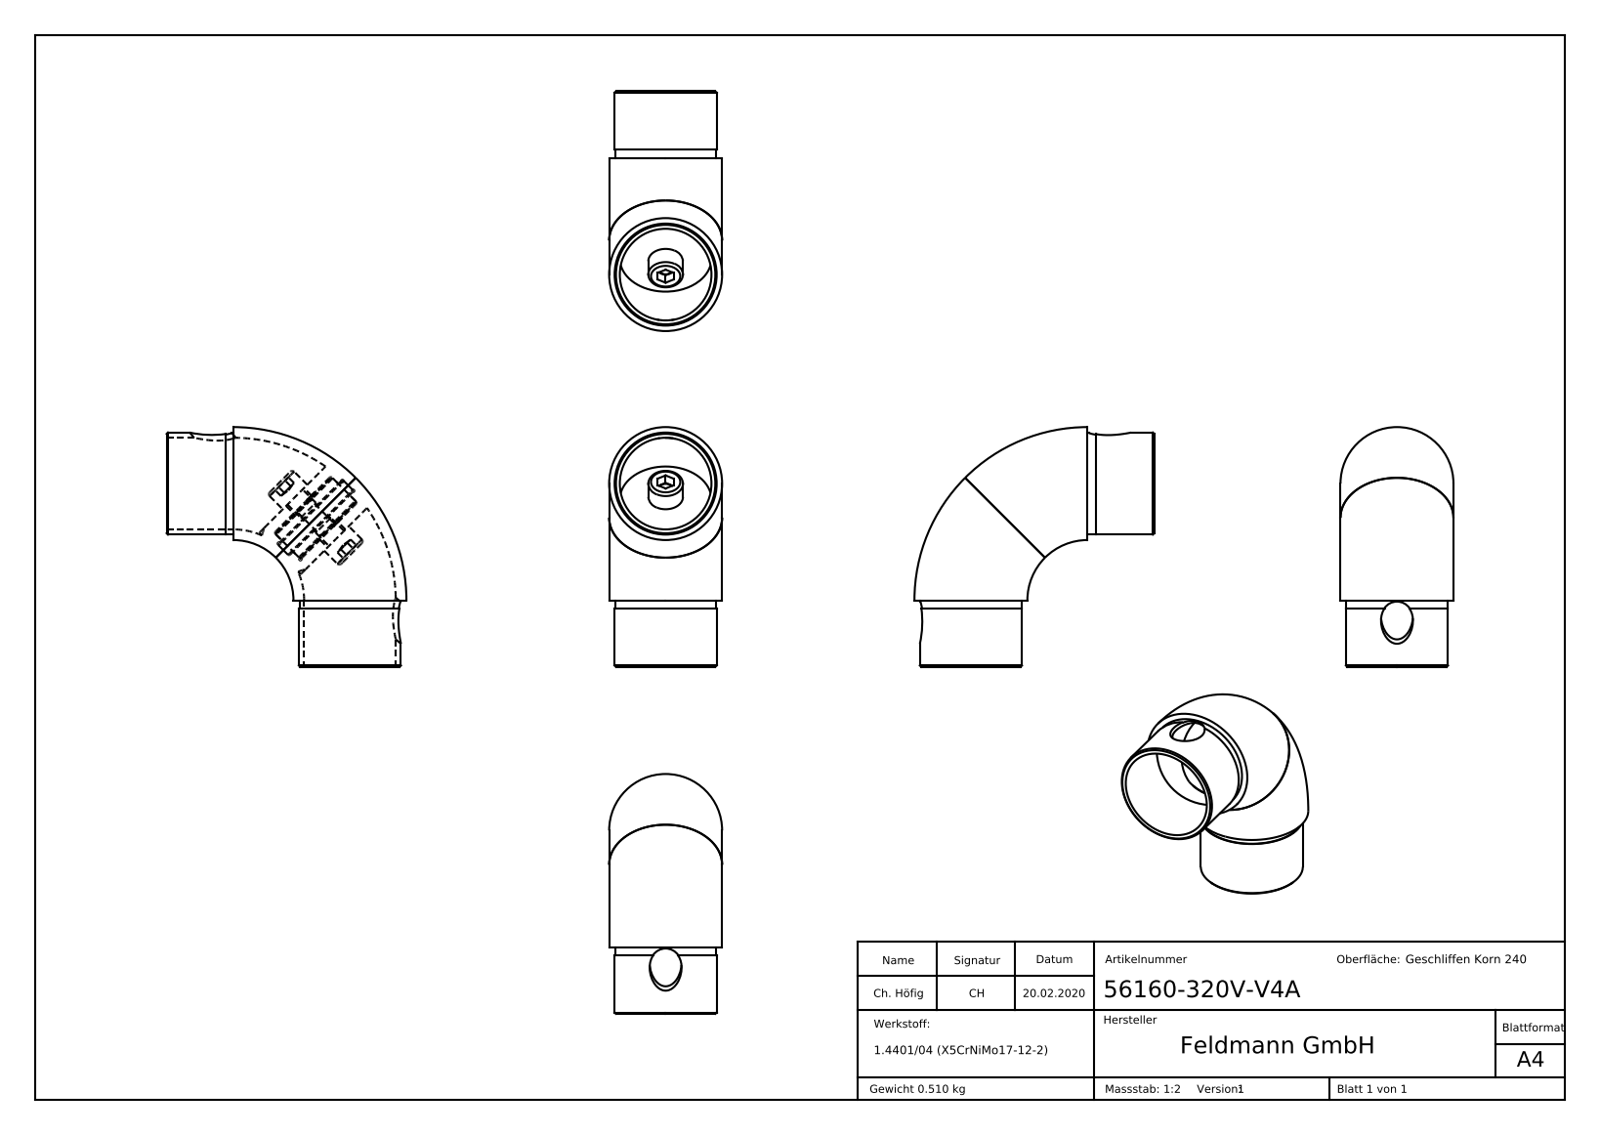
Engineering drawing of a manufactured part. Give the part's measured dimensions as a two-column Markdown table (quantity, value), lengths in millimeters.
| quantity | value |
| --- | --- |
| part name | 5616X-320V Teil1; 5616X-320V Teil2; 56160-320V-V4A; DIN 912 Konfig_DIN 912 M8x8 (+3 more) |
| STEP written by | SolidWorks 2015 (CONFIG_CONTROL_DESIGN) |
| units | millimeters |
| bodies | 5 solids, 628 faces (362 planar, 22 cylindrical, 244 other) |
| overall size | 13955.19 × 12419.37 × 10009.53 |
| volume | 63 824 mm³ |
| surface area | 36 749 mm² |
| round holes (diameter × count) | 34.4 × 4, 9.5 × 2, 12 × 2, 30 × 2, 6.8 × 1 |
| round bosses / shafts (diameter × count) | 38.3 × 2, 37.9 × 2, 13 × 2, 8 × 2 |
| partial cylindrical surfaces (radius × count) | 19 × 2 |
| main face-to-face distances | 6.5, 0.5, 7, 13.5, 21.99, 4, 11, 10.99, 14, 17.5 |
